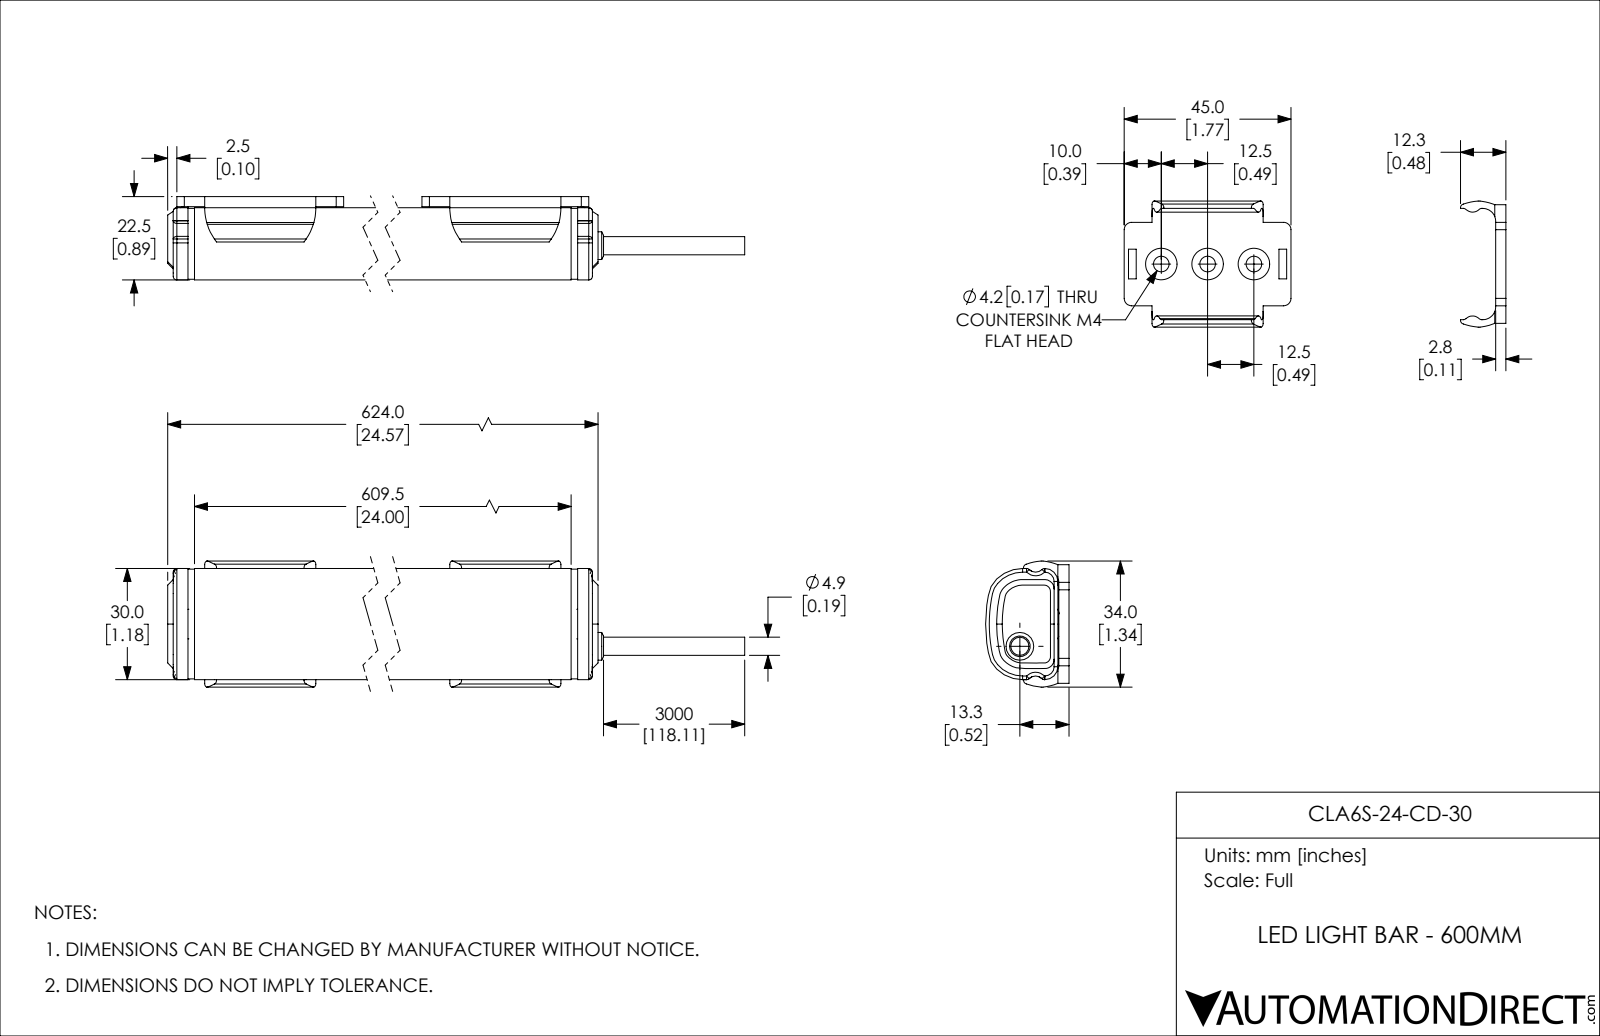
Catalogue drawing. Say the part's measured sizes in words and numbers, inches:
The part is named "CLA6S-24-CD-30". Its 3-D file was written by "SolidWorks 2018 (AUTOMOTIVE_DESIGN)". It is 3 solids with 199 faces: 57 planar, 84 cylindrical and 58 other. Overall it measures 26.126 by 1.339 by 0.886 inches. Its volume is 20.6 cubic inches and its surface area 100.4 square inches. Round holes: 6 of diameter 0.165, 6 of diameter 0.335. Round bosses or shafts: 1 of diameter 0.295, 1 of diameter 0.193. Partial cylindrical surfaces (rounded edges, fillets, slot ends): 10 of radius 0.039, 8 of radius 0.079, 6 of radius 0.591, 2 of radius 0.098, 2 of radius 0.138, 1 of radius 0.433. The main face-to-face distances are 24.567, 0.059, 24.508, 1.26, 0.039, 22.598, 0.118, 0.187, 1.073, 0.295. The hole center spacings are 0.492, 22.598, 0.984, 22.106, 23.091, 21.614, 23.583.
